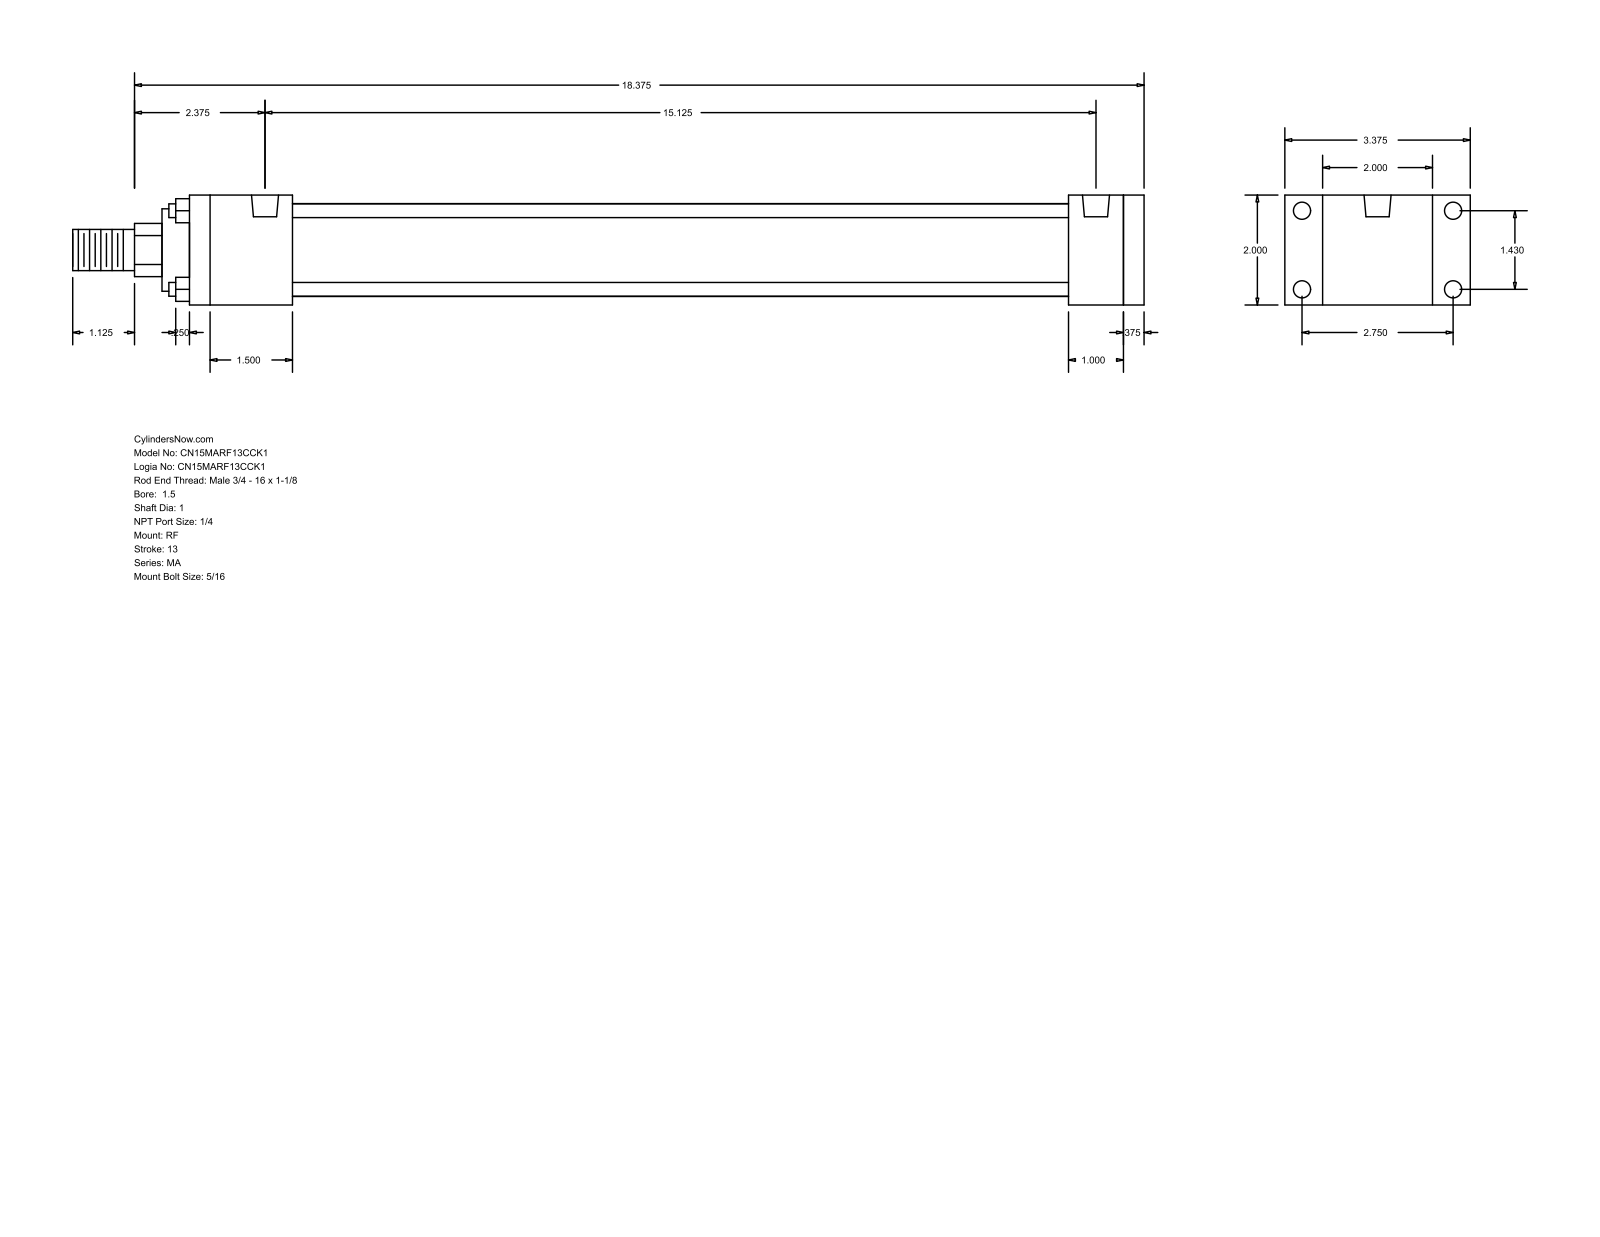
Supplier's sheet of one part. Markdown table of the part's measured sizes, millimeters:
| quantity | value |
| --- | --- |
| part name | MA_RF__0150_1 |
| STEP written by | GSSL Pune (CONFIG_CONTROL_DESIGN) |
| units | millimeters |
| bodies | 0 solids, 92 faces (64 planar, 28 cylindrical, 0 other) |
| overall size | 495.3 × 85.72 × 50.8 |
| round holes (diameter × count) | 7.94 × 8, 12.49 × 2 |
| round bosses / shafts (diameter × count) | 6.35 × 4, 42.93 × 1, 38.1 × 1, 25.4 × 1, 19.05 × 1 |
| partial cylindrical surfaces (radius × count) | 12.29 × 1 |
| main face-to-face distances | 50.8, 9.53, 431.8, 25.4, 441.33, 406.4, 34.93, 47.63, 358.77, 384.17 |
| hole center spacings | 36.32, 69.84, 78.72, 384.17 |
